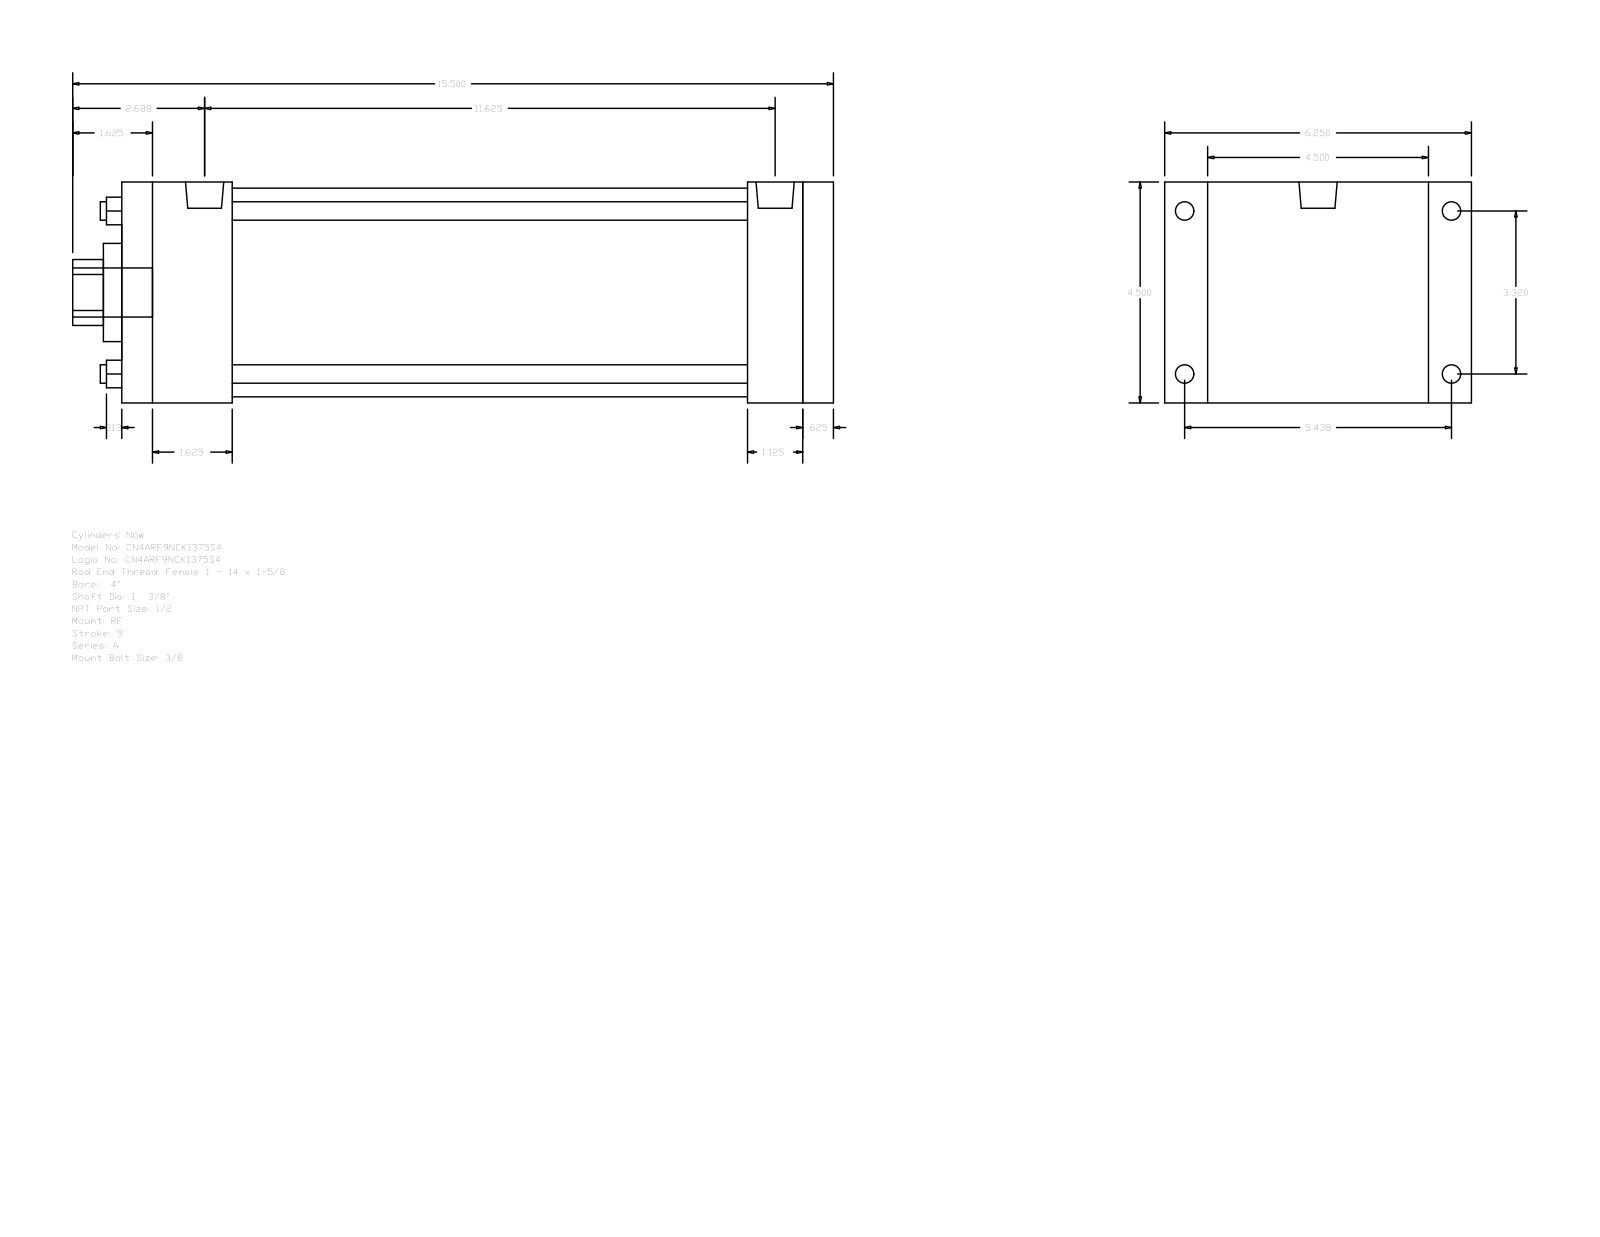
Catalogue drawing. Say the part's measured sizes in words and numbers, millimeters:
The part is named "A_RF__0400_1.375". Its 3-D file was written by "GSSL Pune (CONFIG_CONTROL_DESIGN)". It is 0 solids with 92 faces: 64 planar, 28 cylindrical and 0 other. Overall it measures 393.7 by 158.75 by 114.3 millimeters. Round holes: 4 of diameter 9.53, 1 of diameter 34.92, 1 of diameter 50.8, 1 of diameter 107.95. Round bosses or shafts: 4 of diameter 9.53, 4 of diameter 8.73, 2 of diameter 19.77, 1 of diameter 25.4. Partial cylindrical surfaces (rounded edges, fillets, slot ends): 1 of radius 17.06. The main face-to-face distances are 114.3, 368.3, 15.88, 352.42, 28.57, 22.23, 136.53, 323.85, 44.45, 57.15. The hole center spacings are 59.62, 84.32, 119.25.
